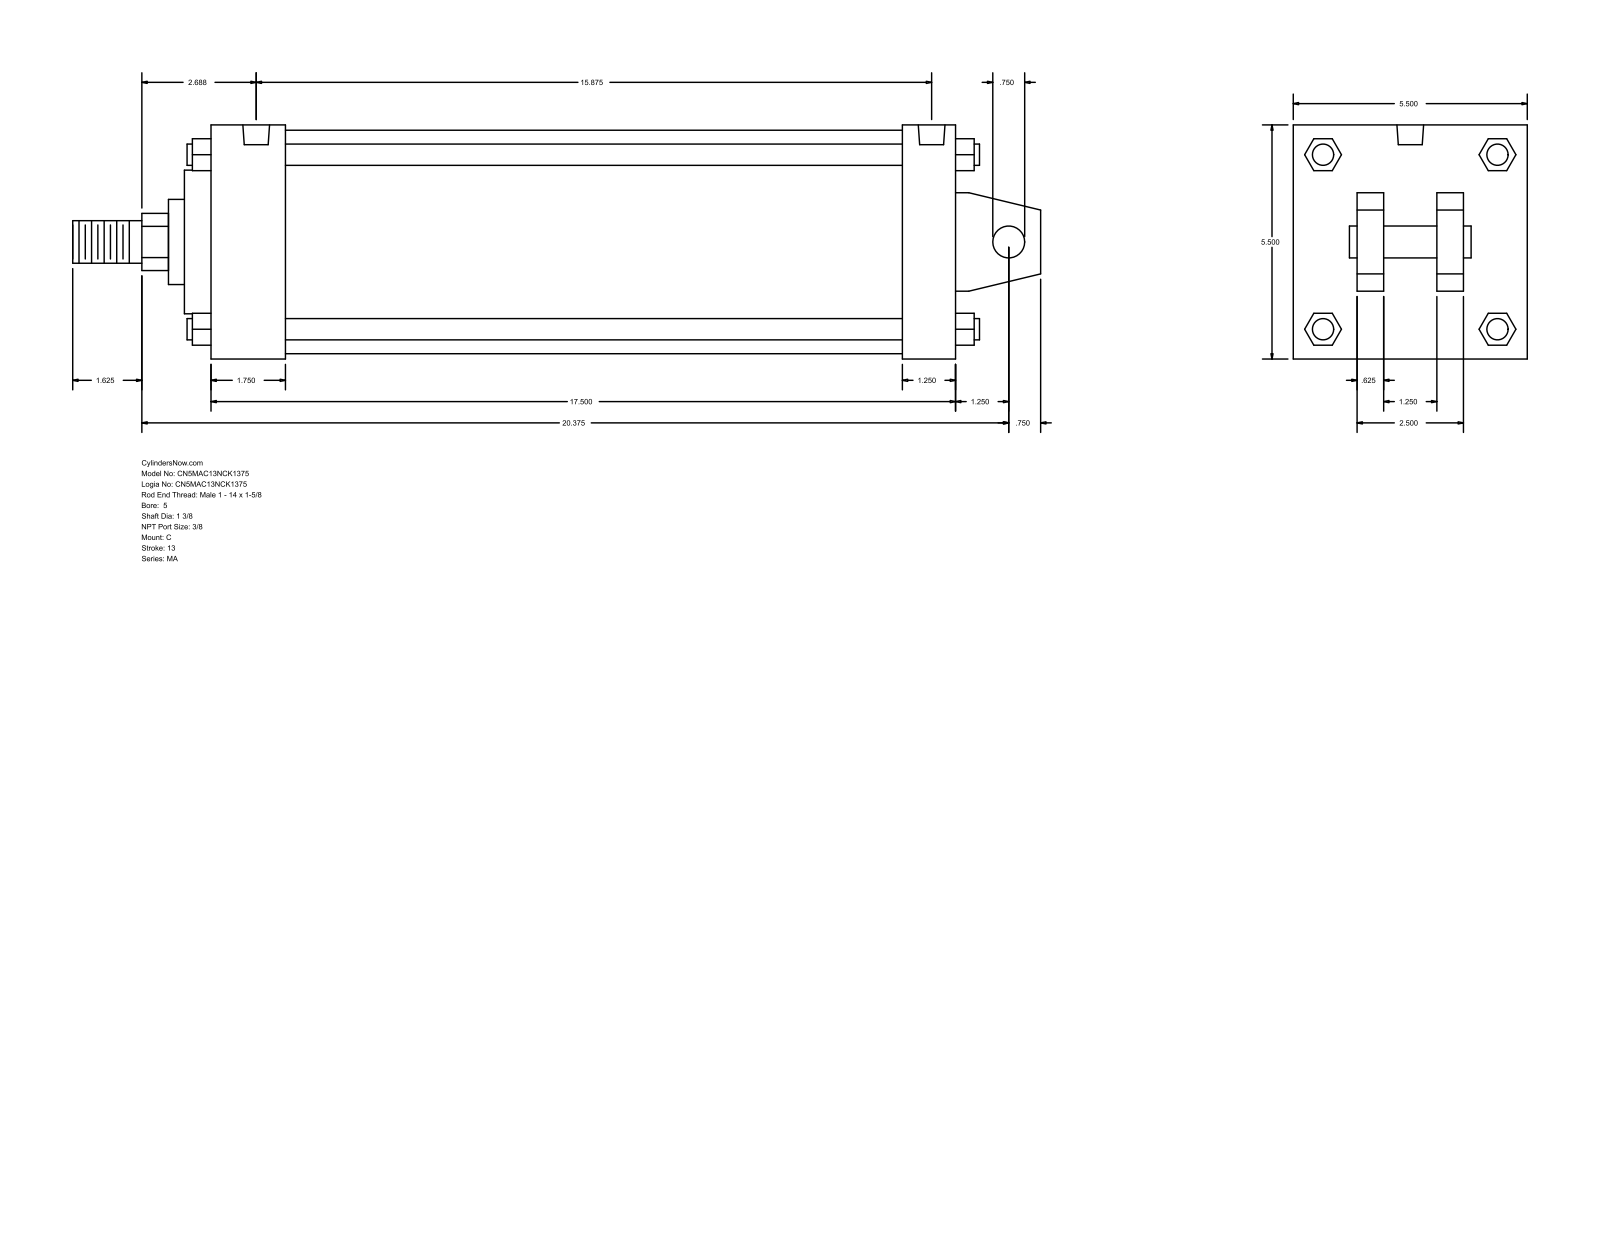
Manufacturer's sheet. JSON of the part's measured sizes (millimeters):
{"part_name": "MA_C__0500_1.375", "step_written_by": "GSSL Pune (CONFIG_CONTROL_DESIGN)", "units": "millimeters", "bodies": {"solids": 0, "faces": 141, "planar": 109, "cylindrical": 32, "other": 0}, "overall_size": [577.85, 139.7, 139.7], "round_holes": [[11.11, 4], [15.93, 2]], "round_bosses_or_shafts": [[12.7, 4], [133.35, 1], [85.72, 1], [50.8, 1], [34.92, 1], [25.4, 1], [19.05, 1]], "partial_cylinders_radius": [[17.06, 1]], "face_to_face_distances": [139.7, 444.5, 15.87, 412.75, 31.75, 44.45, 368.3, 400.05, 53.97, 38.1], "hole_center_spacings": [393.7, 4.76, 4.77, 398.46, 398.47, 403.23]}
